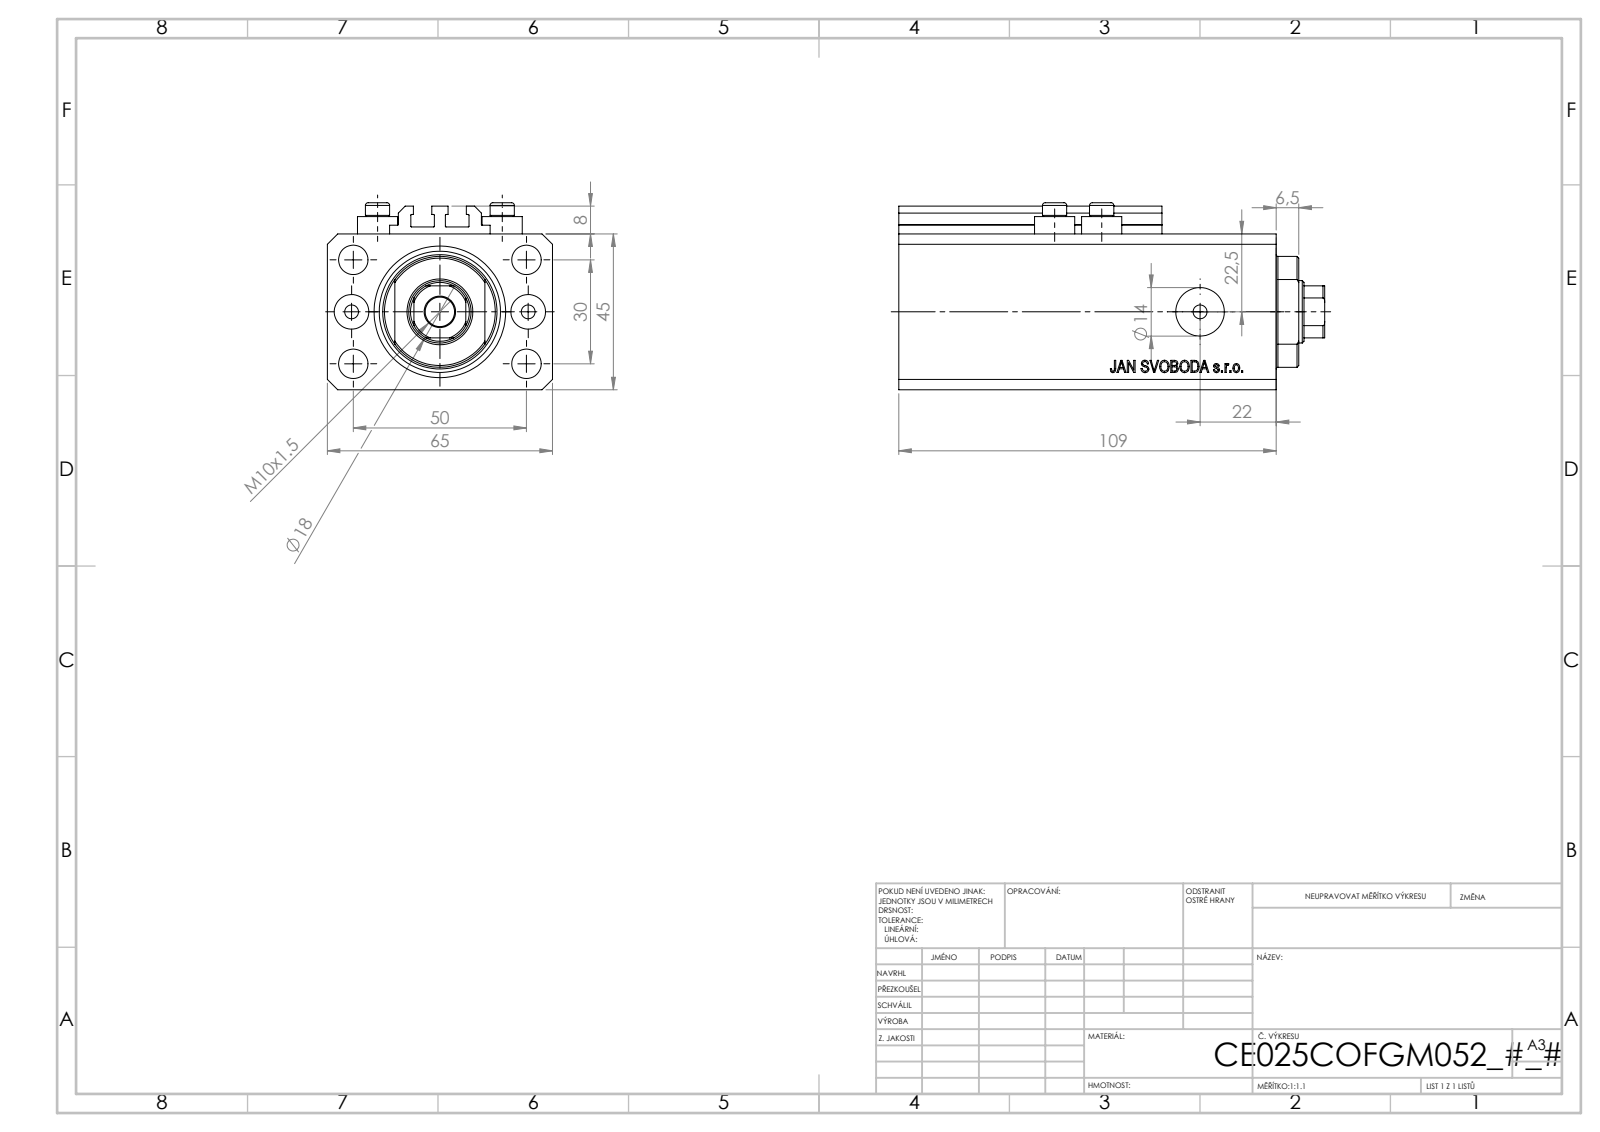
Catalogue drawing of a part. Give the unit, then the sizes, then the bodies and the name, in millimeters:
Units: millimetres
Overall size (bounding box): 123 × 65 × 54
Round holes (diameter × count): ⌀4 ×8, ⌀8.5 ×5, ⌀10 ×2, ⌀14 ×2, ⌀18 ×1, ⌀25 ×1, ⌀38 ×1
Round bosses / shafts (diameter × count): ⌀11.6 ×4, ⌀7 ×4
Partial cylindrical surfaces — rounded edges, fillets, slot ends (radius × count): R0.2 ×10, R8.5 ×1, R16 ×1
Main face-to-face distances: 45, 65, 14, 95, 109, 47, 2.5, 20.5, 10, 2
Hole centre spacings: 15.01, 29.15, 52.68, 13.6, 25.5, 30, 36, 38.48
Volume: 294 172 mm³ · Surface area: 75 047 mm²
Bodies: 8 solids, 1034 faces (504 planar, 86 cylindrical, 444 other)
Part name (STEP PRODUCT): ALLEN BOLT V250CE; V250CE_C_Body; V250CE_C_VCP; V250CE_VC_C
STEP written by: SolidWorks 2019 (CONFIG_CONTROL_DESIGN)
